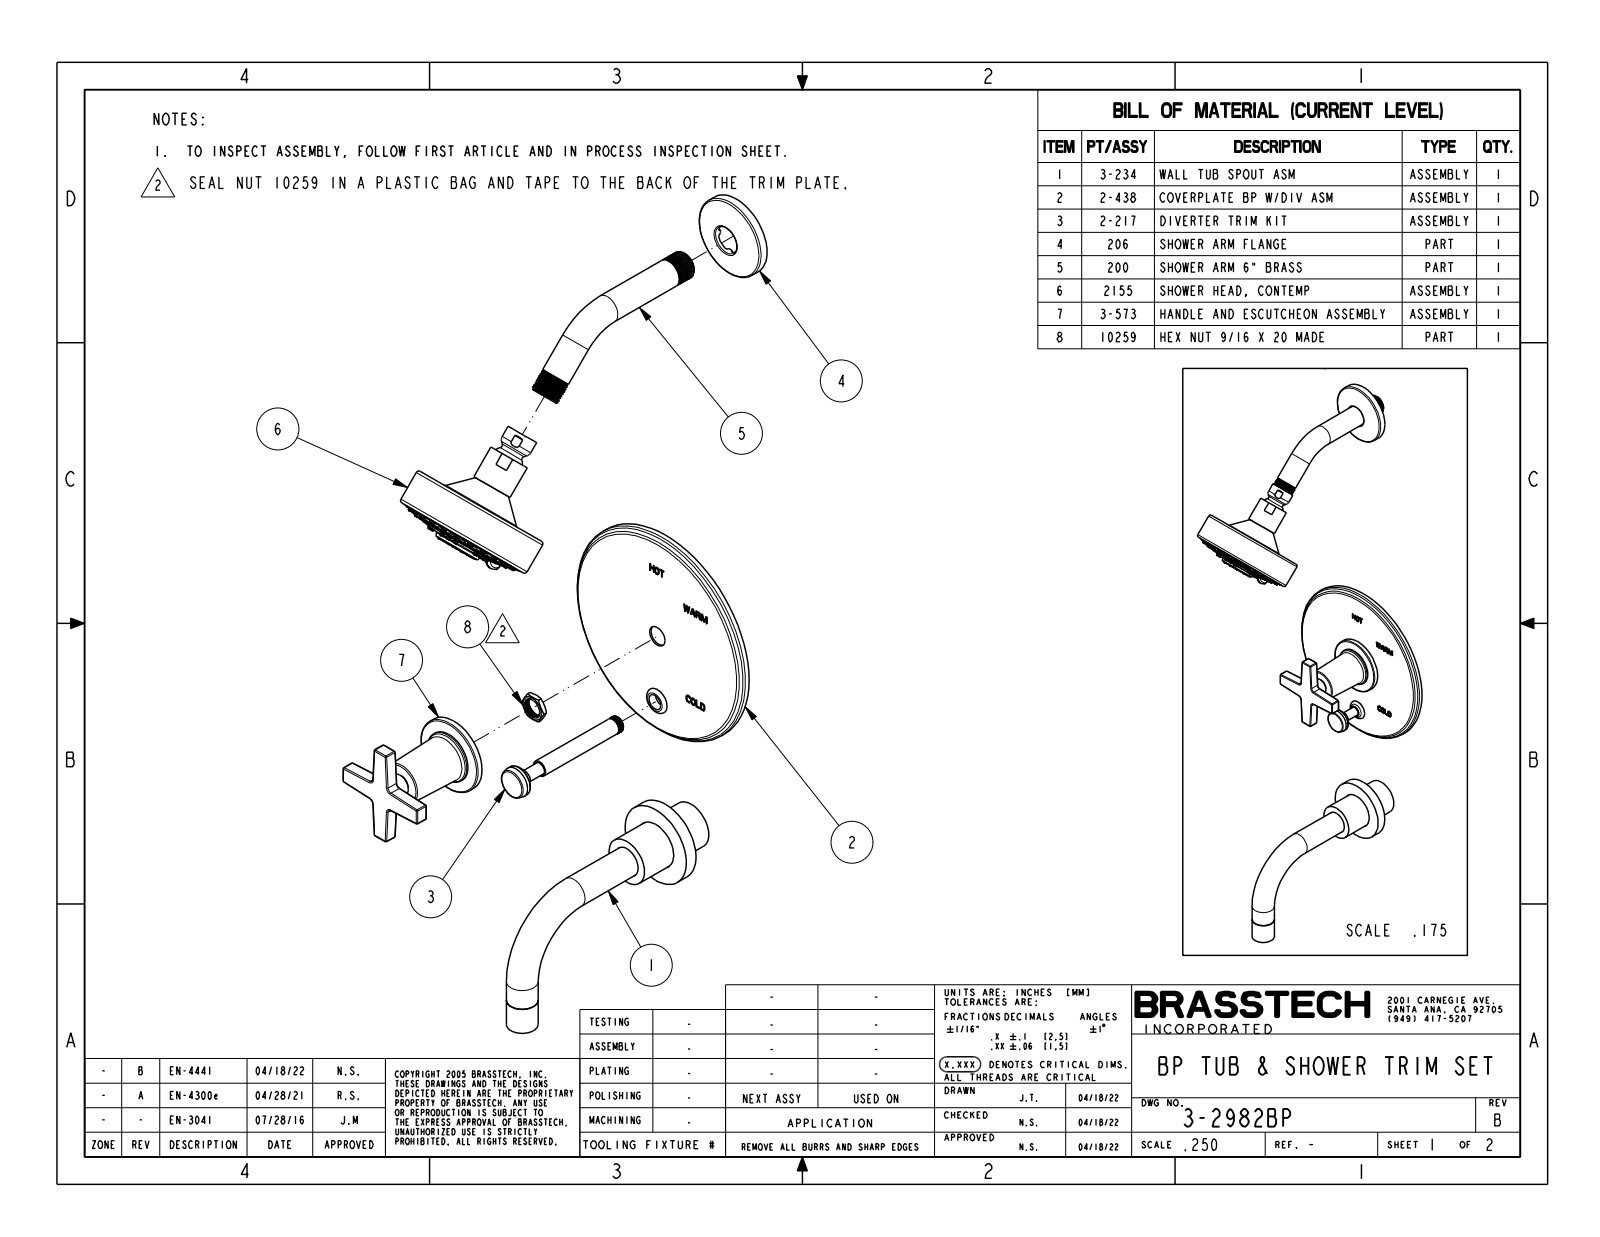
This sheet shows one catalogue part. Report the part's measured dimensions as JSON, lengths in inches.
{"part_name": "3-2982BP", "step_written_by": "CREO PARAMETRIC BY PTC INC, 2018400 (CONFIG_CONTROL_DESIGN)", "units": "inches", "bodies": {"solids": 3, "faces": 1446, "planar": 417, "cylindrical": 252, "other": 777}, "overall_size": [23.63, 8.175, 6.5], "volume_in3": 44.16, "surface_area_in2": 205.6, "round_holes": [[0.059, 8], [0.925, 1]], "round_bosses_or_shafts": [[0.142, 39], [0.165, 23], [0.875, 2], [0.813, 2], [6.5, 1], [4, 1], [3.724, 1], [2.38, 1]], "partial_cylinders_radius": [[0.03, 32], [0.079, 8], [0.125, 4], [0.02, 2], [0.138, 1], [0.472, 1], [0.512, 1], [0.63, 1]], "face_to_face_distances": [0.313, 0.062, 0.375, 0.125, 3.183, 2.87, 2.808, 0.187, 0.5, 2.683], "hole_center_spacings": [0.443, 0.579, 0.818, 0.819, 1.069, 0.443, 0.578, 1.069]}
